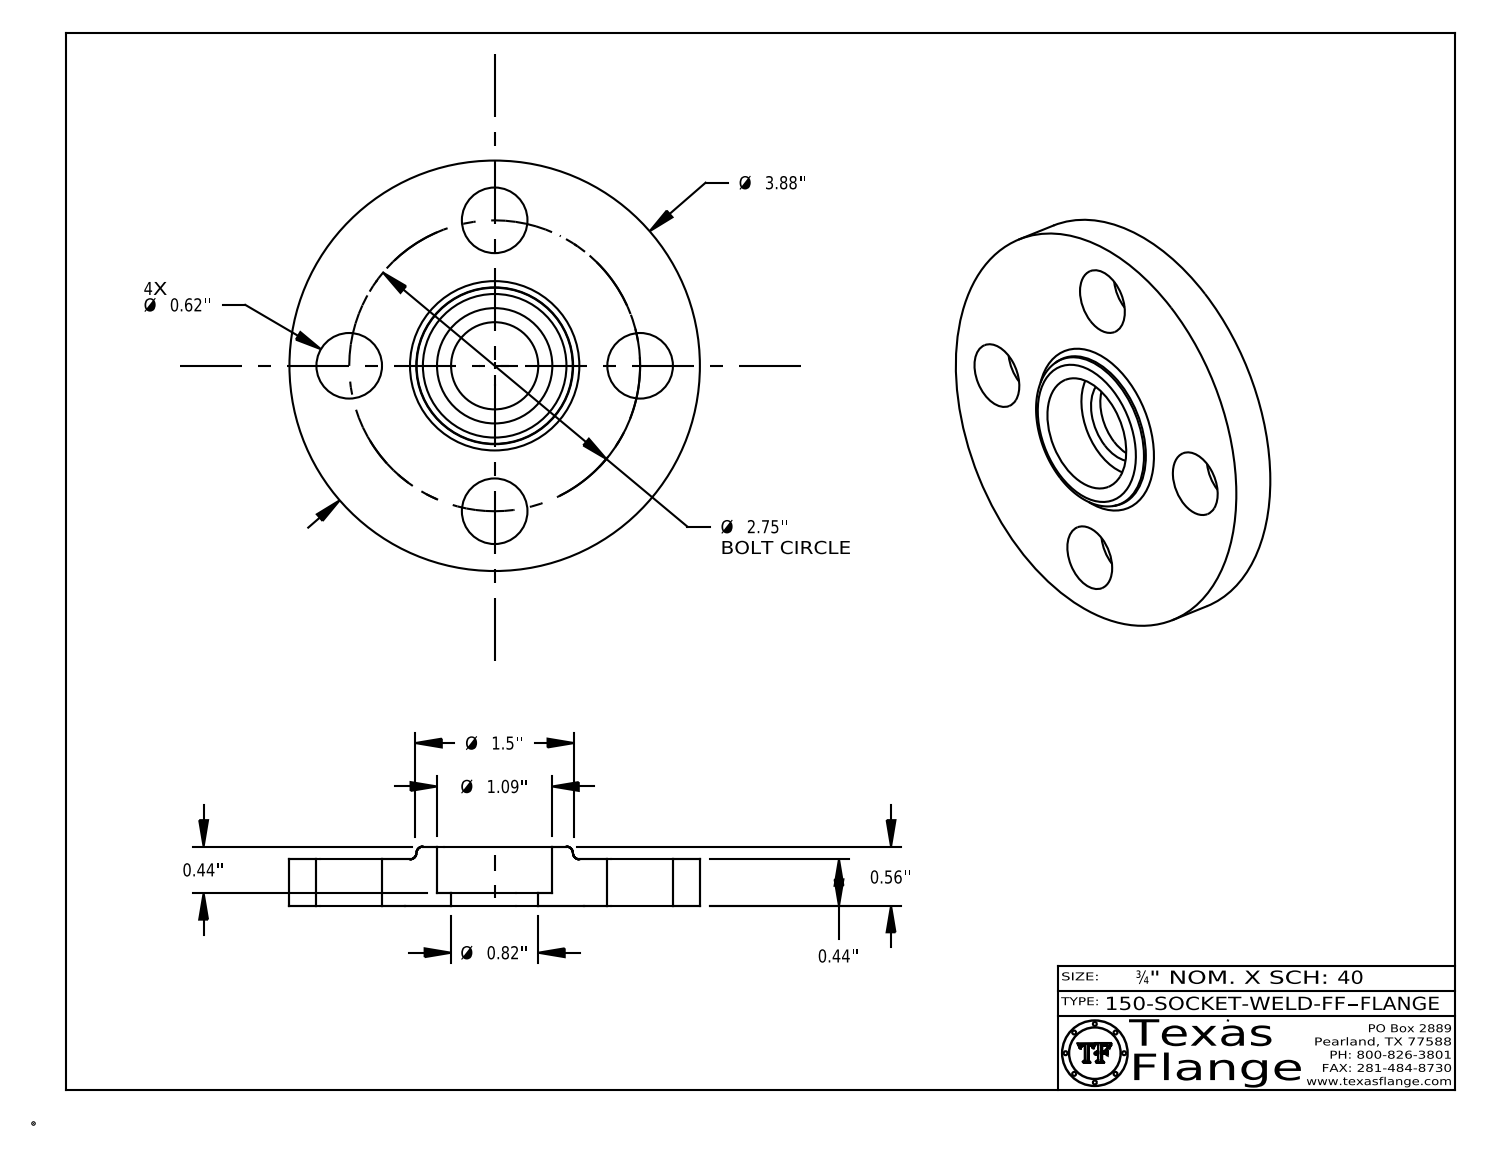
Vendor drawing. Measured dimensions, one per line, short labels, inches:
name: 150-SOCKET-WELD-FF
written by: CATIA V5 STEP AP214 (AUTOMOTIVE_DESIGN)
unit: in
bodies: 1 solid, 410 faces (370 planar, 34 cylindrical, 6 other)
size: 3.88 × 3.88 × 0.56
volume: 4.402 in³; area: 31.18 in²
holes: 4× ⌀0.62, 1× ⌀0.495, 1× ⌀0.824, 1× ⌀1.09
bosses: 8× ⌀0.03, 1× ⌀3.88, 1× ⌀0.39
face distances: 0.44, 0.56, 0.12, 0.12, 0.32, 0.44, 0.425, 0.305, 0.015, 0.135
hole spacings: 1.375, 1.945, 1.052, 2.541, 2.75
